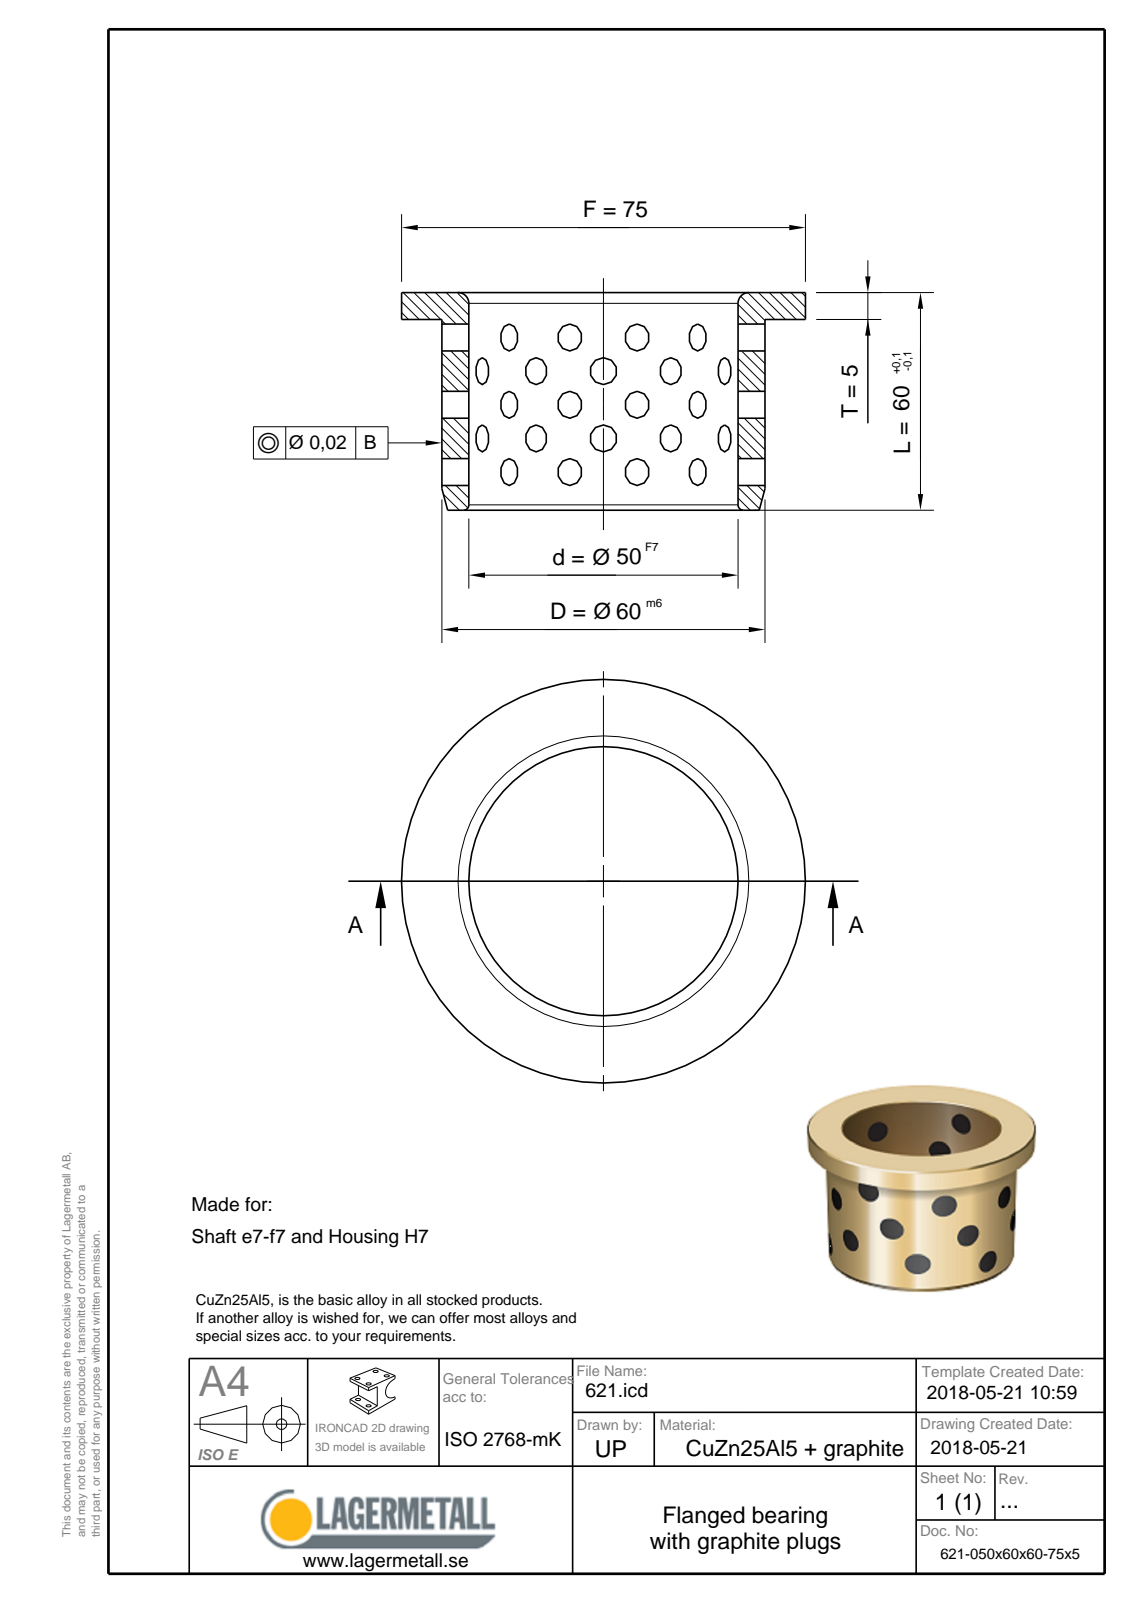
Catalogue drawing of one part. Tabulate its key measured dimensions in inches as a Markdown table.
| quantity | value |
| --- | --- |
| part name | 621-050x60x60-75x5 |
| STEP written by | Spatial InterOp 3D (CONFIG_CONTROL_DESIGN) |
| units | inches |
| bodies | 1 solid, 9 faces (3 planar, 3 cylindrical, 3 other) |
| overall size | 2.953 × 2.953 × 2.362 |
| volume | 3.618 in³ |
| surface area | 39.49 in² |
| round holes (diameter × count) | 1.969 × 1 |
| round bosses / shafts (diameter × count) | 2.953 × 1, 2.362 × 1 |
| main face-to-face distances | 0.197, 2.165, 2.362 |
